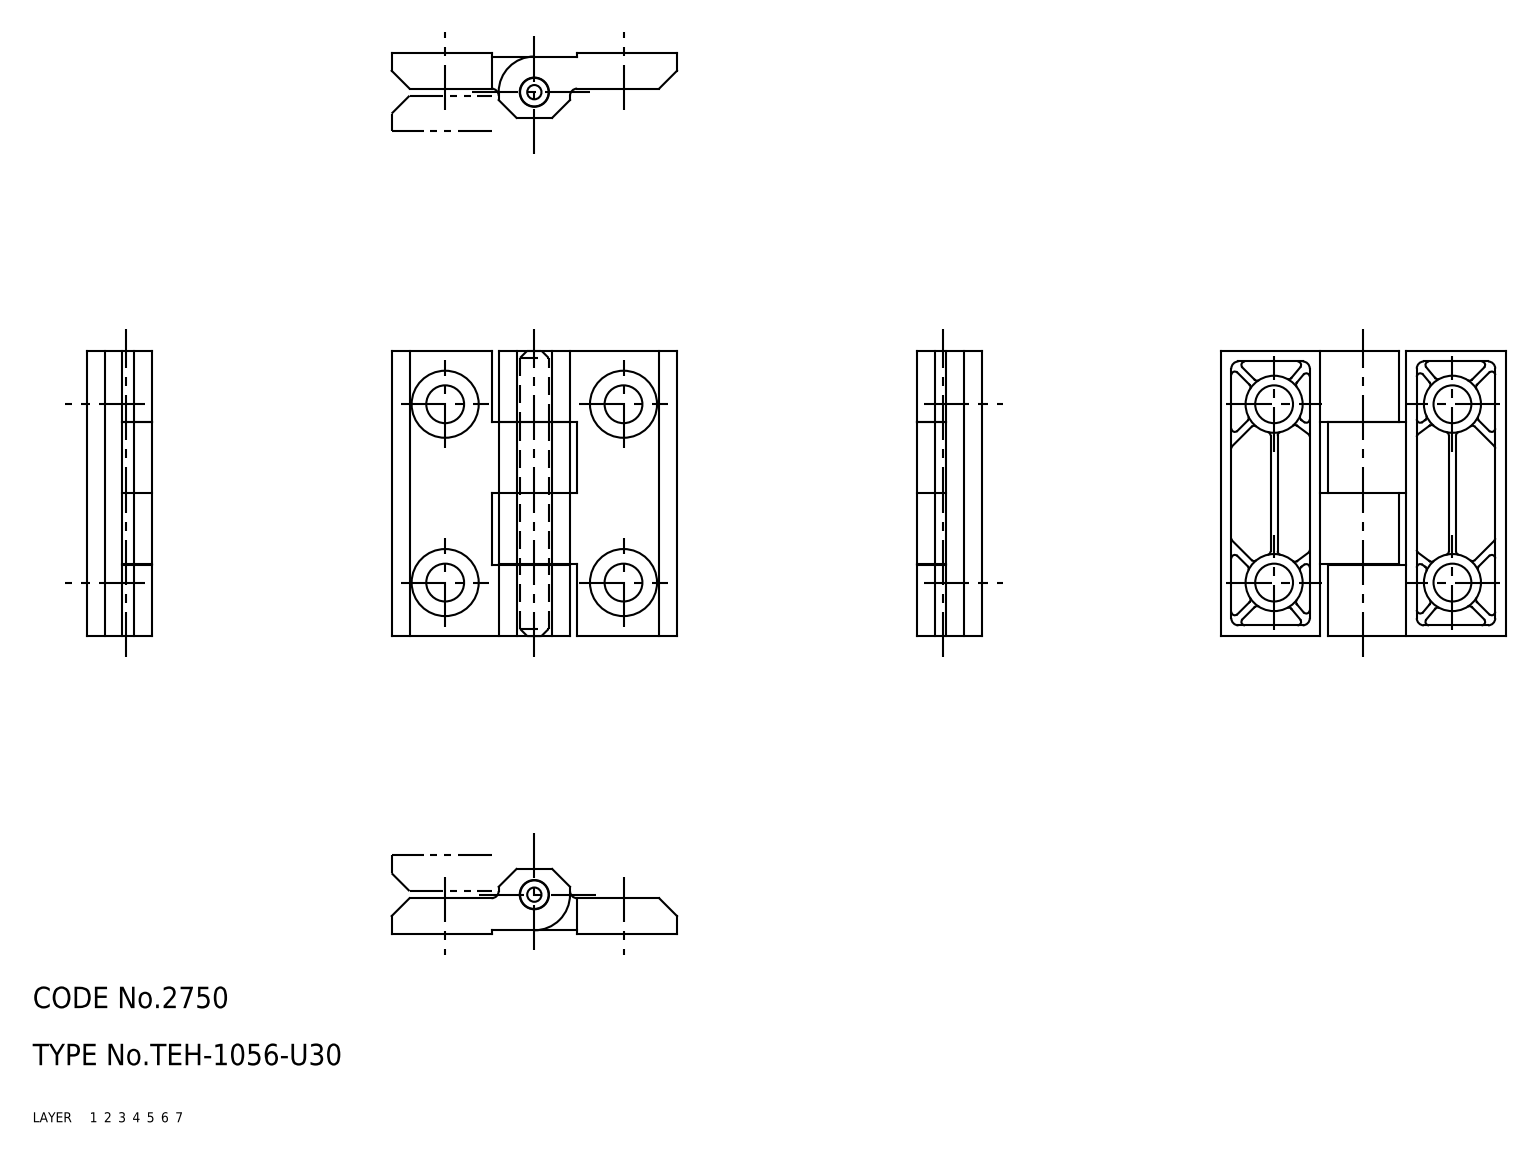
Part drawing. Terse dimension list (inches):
name: shaft; hinge pieces_B; hinge pieces_A; TEH_1056_U30_9321_36
written by: CADfix (AUTOMOTIVE_DESIGN)
unit: in
bodies: 3 solids, 251 faces (0 planar, 0 cylindrical, 251 other)
size: 1.575 × 1.575 × 0.358
volume: 0.394 in³; area: 10.34 in²
